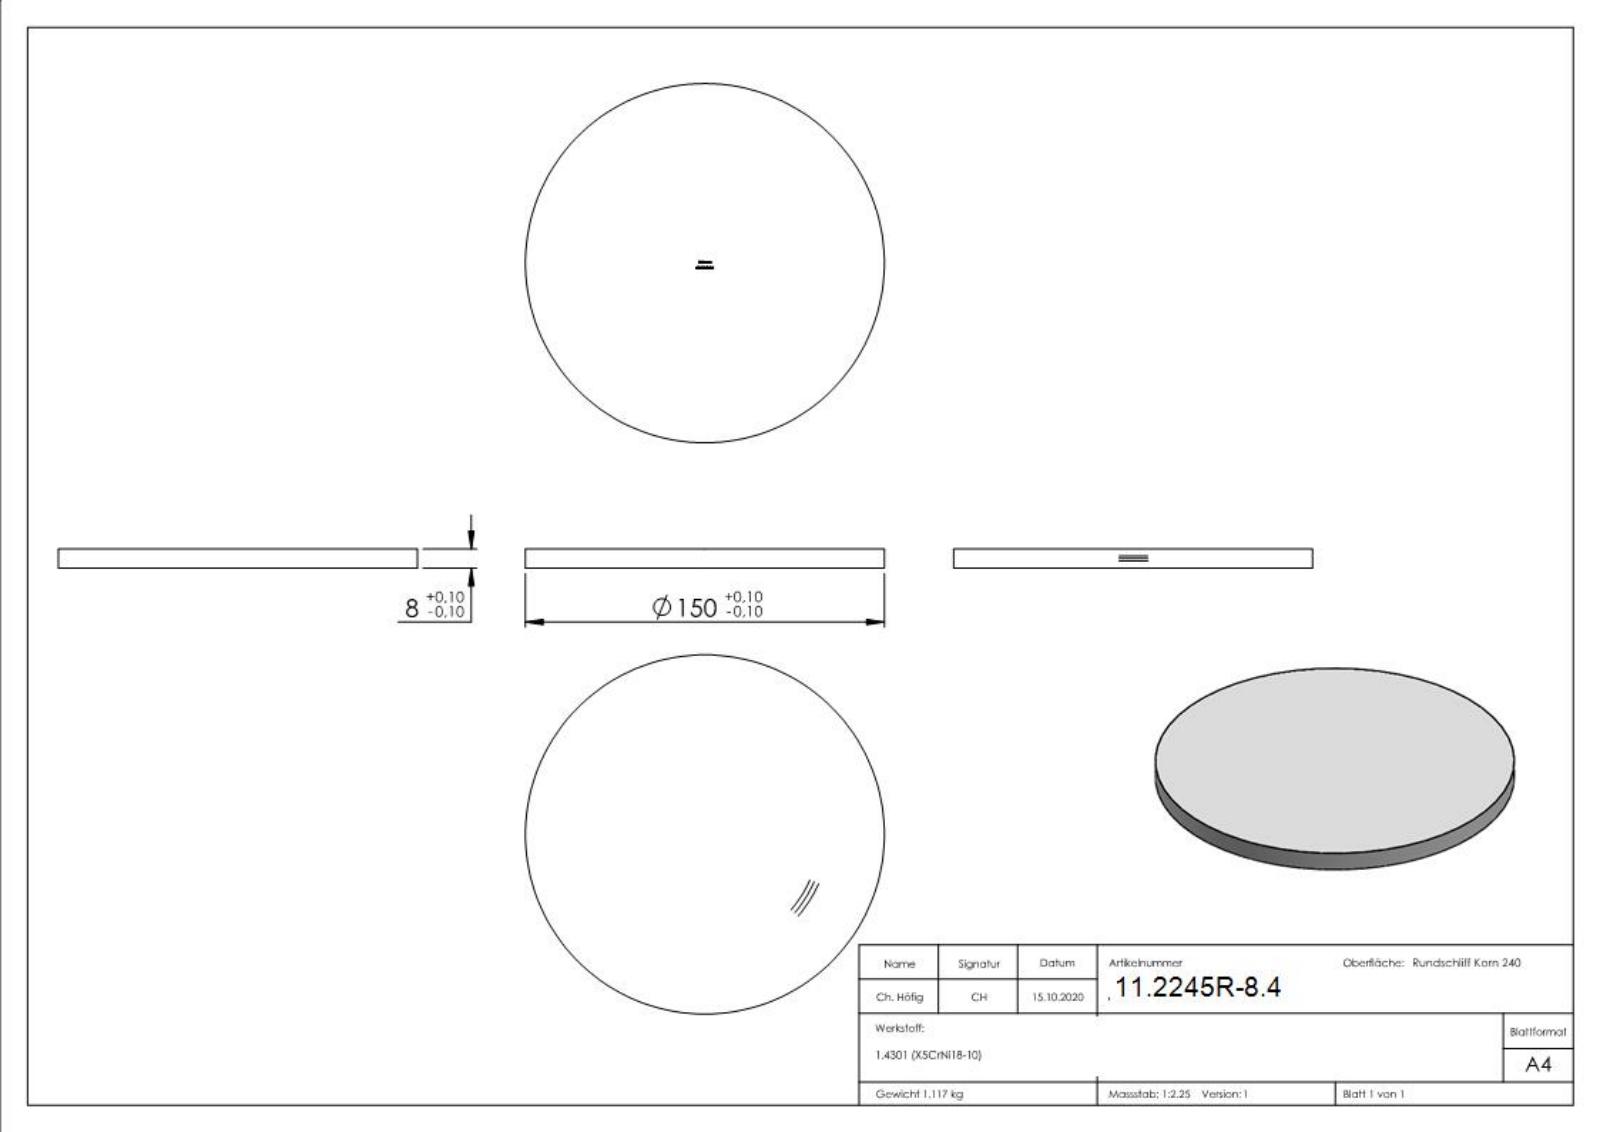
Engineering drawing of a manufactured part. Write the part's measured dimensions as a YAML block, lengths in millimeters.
part_name: "53150-240-8-R"
step_written_by: "SolidWorks 2018 (CONFIG_CONTROL_DESIGN)"
units: millimeters
bodies: {solids: 1, faces: 275, planar: 149, cylindrical: 2, other: 124}
overall_size: [150, 150, 8]
volume: 141371
surface_area: 39120
round_bosses_or_shafts:
  - {diameter: 150, count: 1}
face_to_face_distances: [8, 7.9, 0.71, 0.45, 0.53, 1.78, 0.83, 2.77, 0.79, 1.88]
